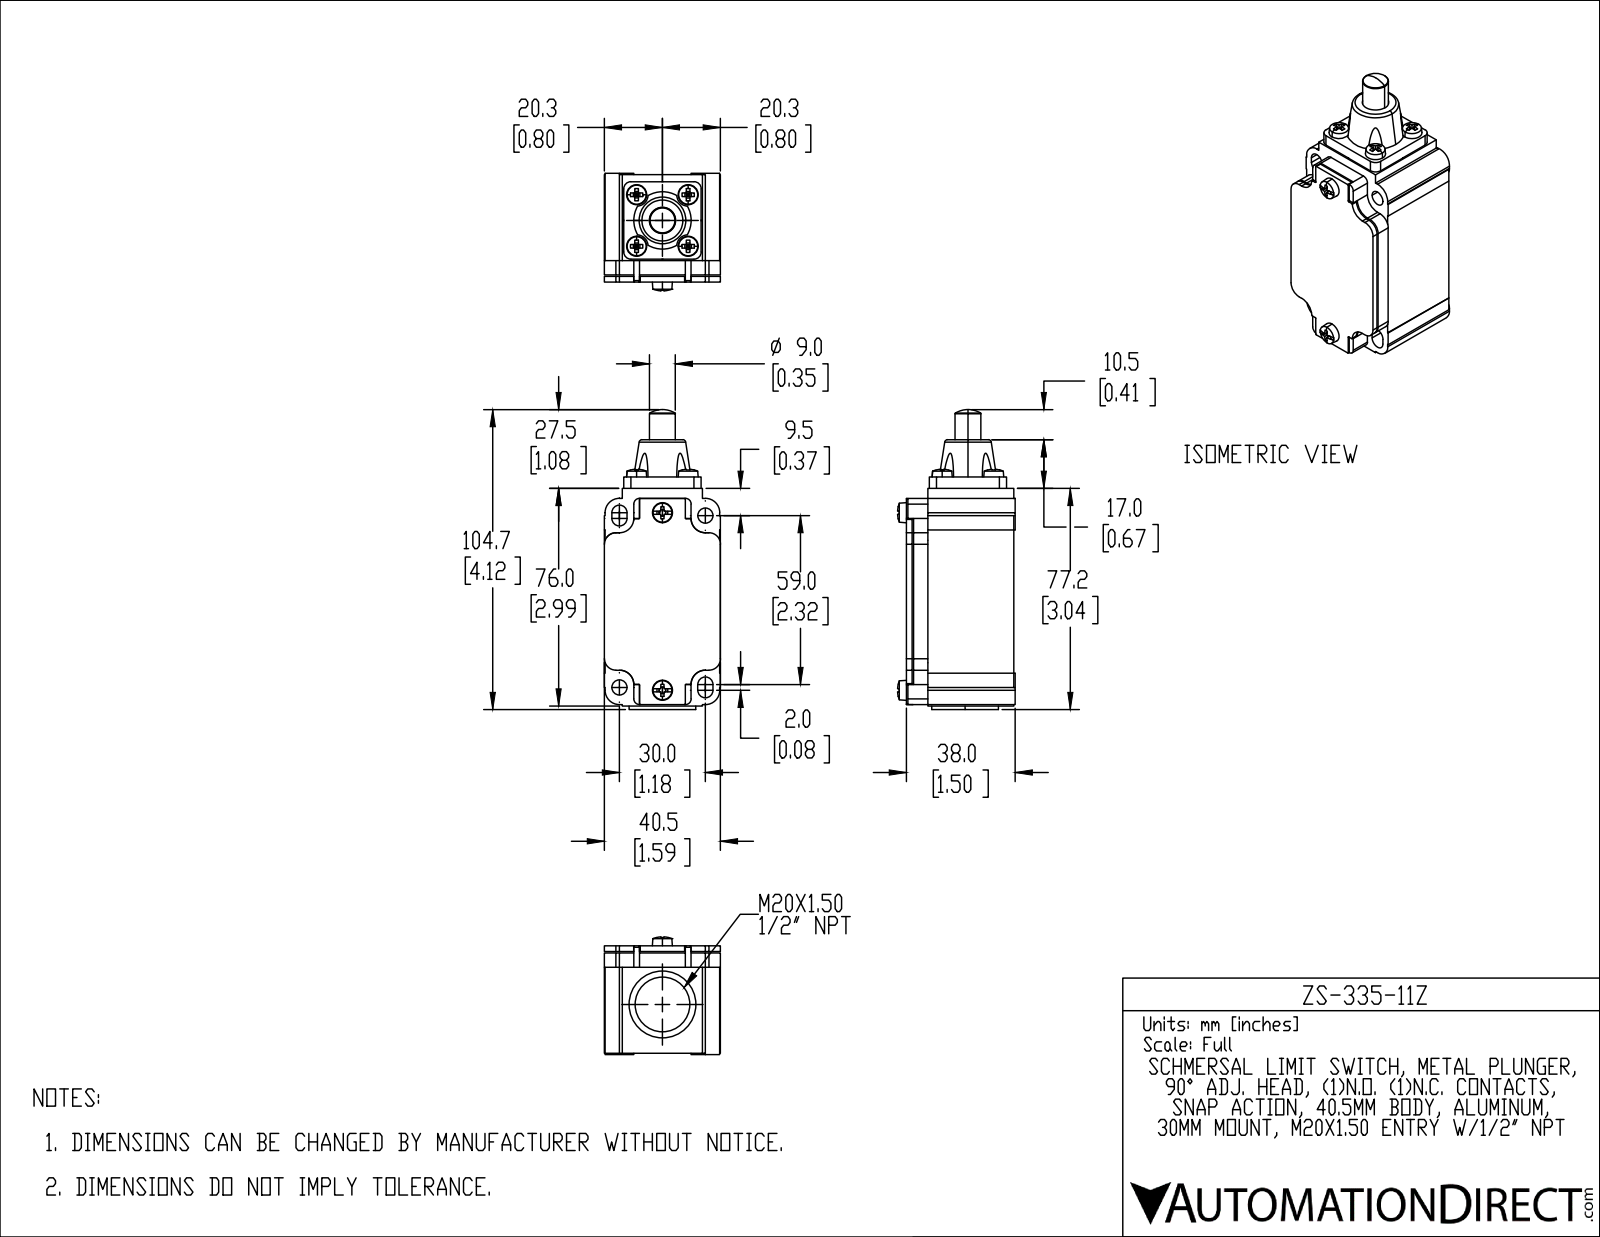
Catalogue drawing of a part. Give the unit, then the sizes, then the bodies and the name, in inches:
Units: inches
Overall size (bounding box): 4.122 × 1.617 × 1.594
Round holes (diameter × count): ⌀0.081 ×4, ⌀0.15 ×4, ⌀0.169 ×4, ⌀0.209 ×2, ⌀0.362 ×1, ⌀0.551 ×1, ⌀0.591 ×1, ⌀0.711 ×1, ⌀0.75 ×1
Round bosses / shafts (diameter × count): ⌀0.917 ×1, ⌀0.709 ×1, ⌀0.354 ×1
Partial cylindrical surfaces — rounded edges, fillets, slot ends (radius × count): R0.157 ×16, R0.01 ×12, R0.197 ×12, R0.079 ×4, R0.098 ×4, R0.104 ×4, R0.197 ×4
Main face-to-face distances: 0.02, 0.098, 1.398, 1.378, 0.079, 1.476, 1.181, 0.197, 0.295, 0.217
Hole centre spacings: 0.38, 0.918, 0.492, 0.501, 0.696, 0.709, 0.474, 0.494
Volume: 6.471 in³ · Surface area: 39.86 in²
Bodies: 1 solid, 449 faces (284 planar, 113 cylindrical, 52 other)
Part name (STEP PRODUCT): ZS-335-11Z
STEP written by: SolidWorks 2019 (AUTOMOTIVE_DESIGN)
